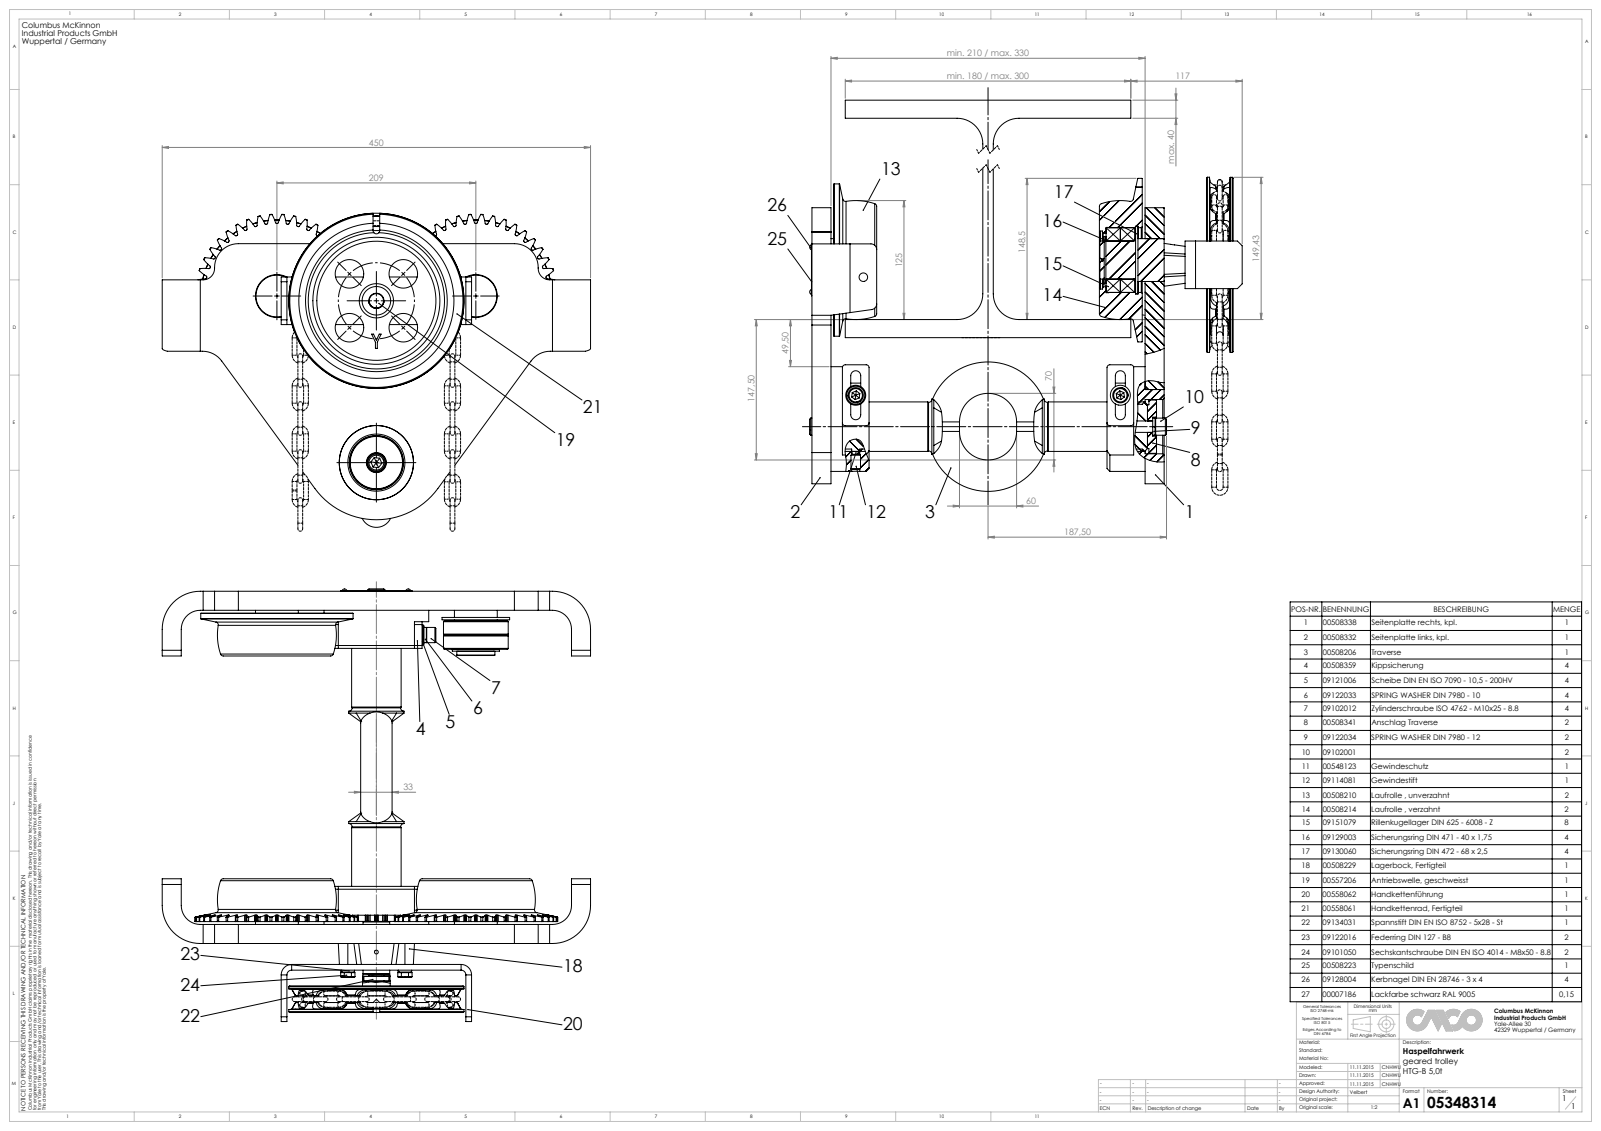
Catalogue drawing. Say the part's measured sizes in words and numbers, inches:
The part is named "05348314". Its 3-D file was written by "SolidWorks 2015 (AUTOMOTIVE_DESIGN)". It is 0 solids with 1058 faces: 271 planar, 524 cylindrical and 263 other. Overall it measures 18.329 by 17.894 by 17.717 inches. Round holes: 4 of diameter 1.181, 2 of diameter 0.354, 2 of diameter 1.772, 2 of diameter 2.205, 2 of diameter 2.283, 2 of diameter 2.402, 1 of diameter 0.118, 1 of diameter 0.197, 1 of diameter 0.236, 1 of diameter 0.335, 1 of diameter 0.63, 1 of diameter 0.787. Round bosses or shafts: 26 of diameter 0.197, 2 of diameter 6.299, 2 of diameter 1.948, 2 of diameter 1.575, 2 of diameter 0.827, 2 of diameter 0.63, 2 of diameter 0.394, 1 of diameter 7.244. Partial cylindrical surfaces (rounded edges, fillets, slot ends): 112 of radius 1.575, 100 of radius 0.039, 10 of radius 0.394, 9 of radius 0.059, 6 of radius 0.118, 4 of radius 0.207, 4 of radius 0.236, 4 of radius 0.787. The main face-to-face distances are 0.787, 0.748, 11.063, 13.78, 7.067, 7.5, 6.28, 6.713, 11.811, 12.992. The hole center spacings are 2.227, 1.115, 1.574, 1.576, 2.55, 3.138, 3.149, 3.274.
